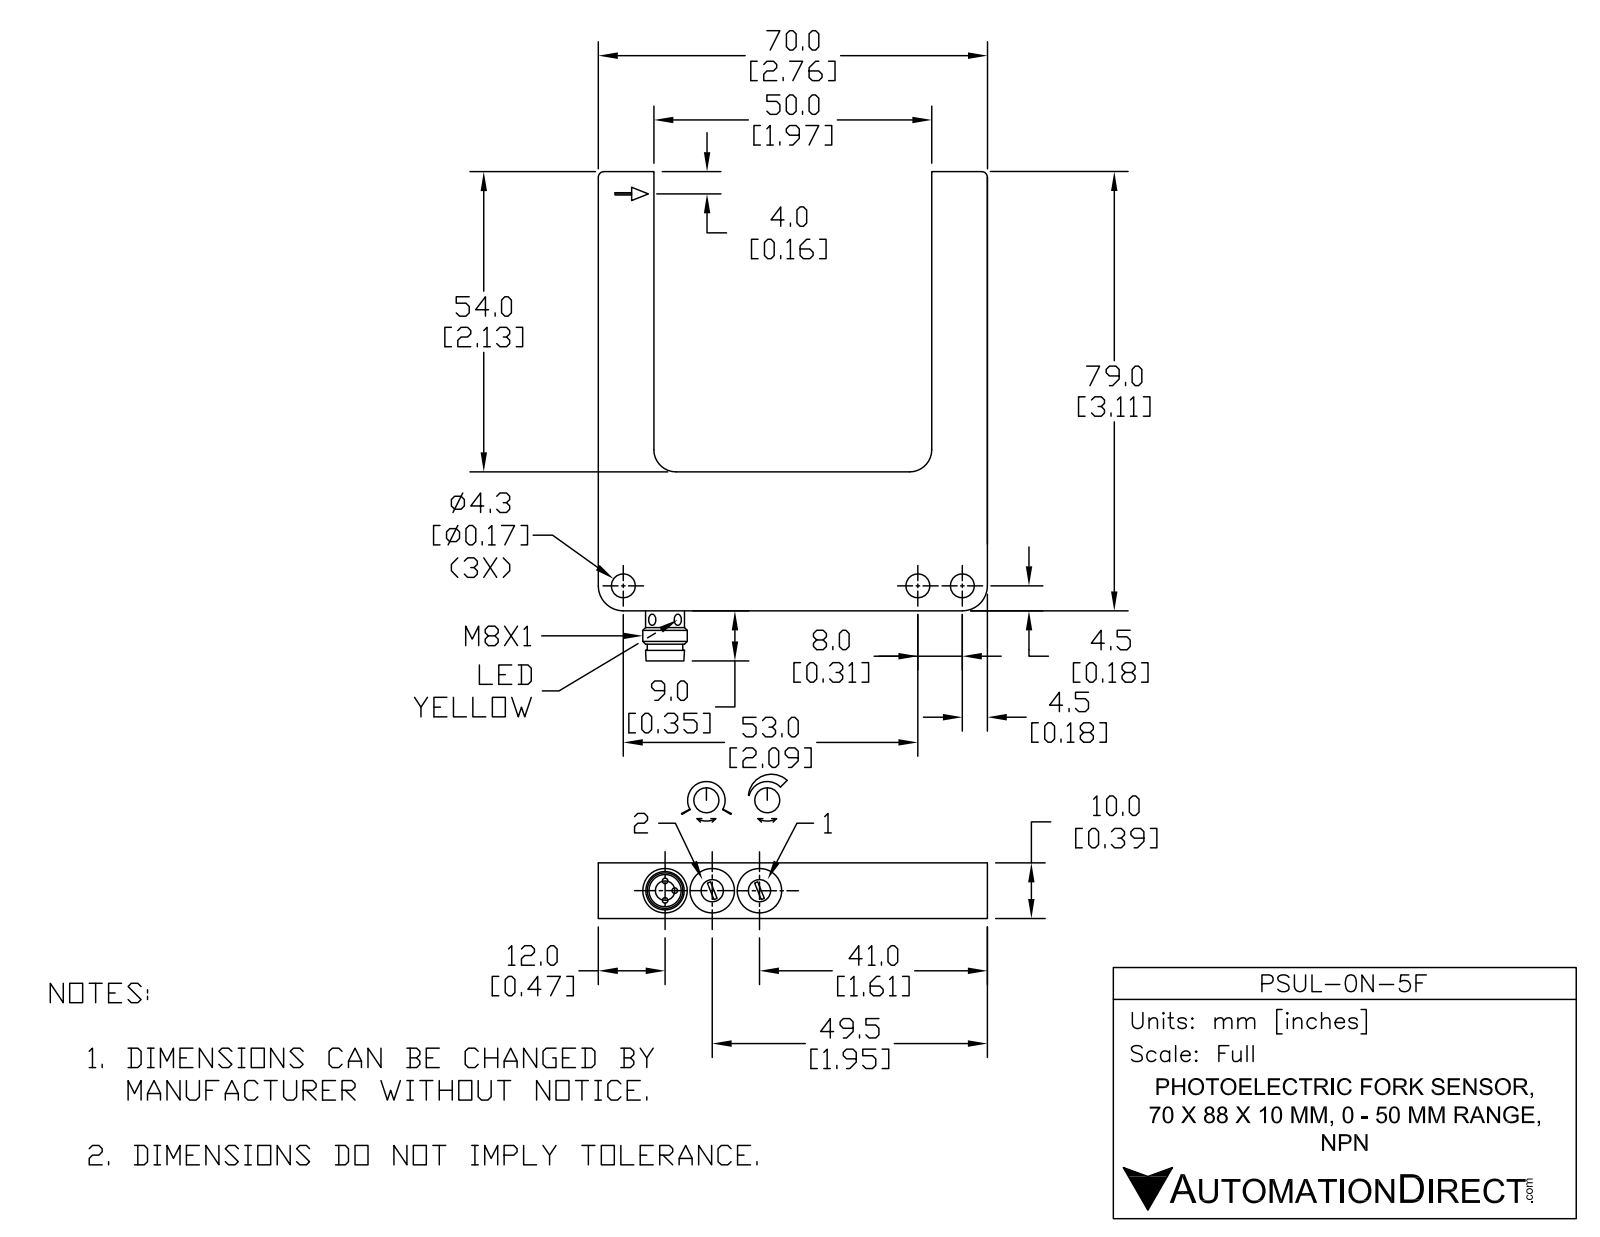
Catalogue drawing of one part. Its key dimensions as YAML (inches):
part_name: "PSUL-0N-5F"
step_written_by: "SolidWorks 2019 (AUTOMOTIVE_DESIGN)"
units: inches
bodies: {solids: 1, faces: 95, planar: 35, cylindrical: 48, other: 12}
overall_size: [3.465, 2.756, 0.394]
volume: 1.712
surface_area: 16
round_holes:
  - {diameter: 0.169, count: 3}
  - {diameter: 0.079, count: 2}
  - {diameter: 0.157, count: 2}
  - {diameter: 0.315, count: 2}
  - {diameter: 0.228, count: 1}
round_bosses_or_shafts:
  - {diameter: 0.039, count: 3}
  - {diameter: 0.315, count: 1}
  - {diameter: 0.267, count: 1}
partial_cylinders:
  - {radius: 0.02, count: 2}
  - {radius: 0.039, count: 2}
  - {radius: 0.063, count: 2}
  - {radius: 0.157, count: 2}
  - {radius: 0.177, count: 2}
face_to_face_distances: [0.394, 2.362, 2.756, 1.969, 0.984, 2.126, 3.11, 3.106, 0.98, 0.157]
hole_center_spacings: [0.335, 0.315, 0.669, 2.087, 2.402]
